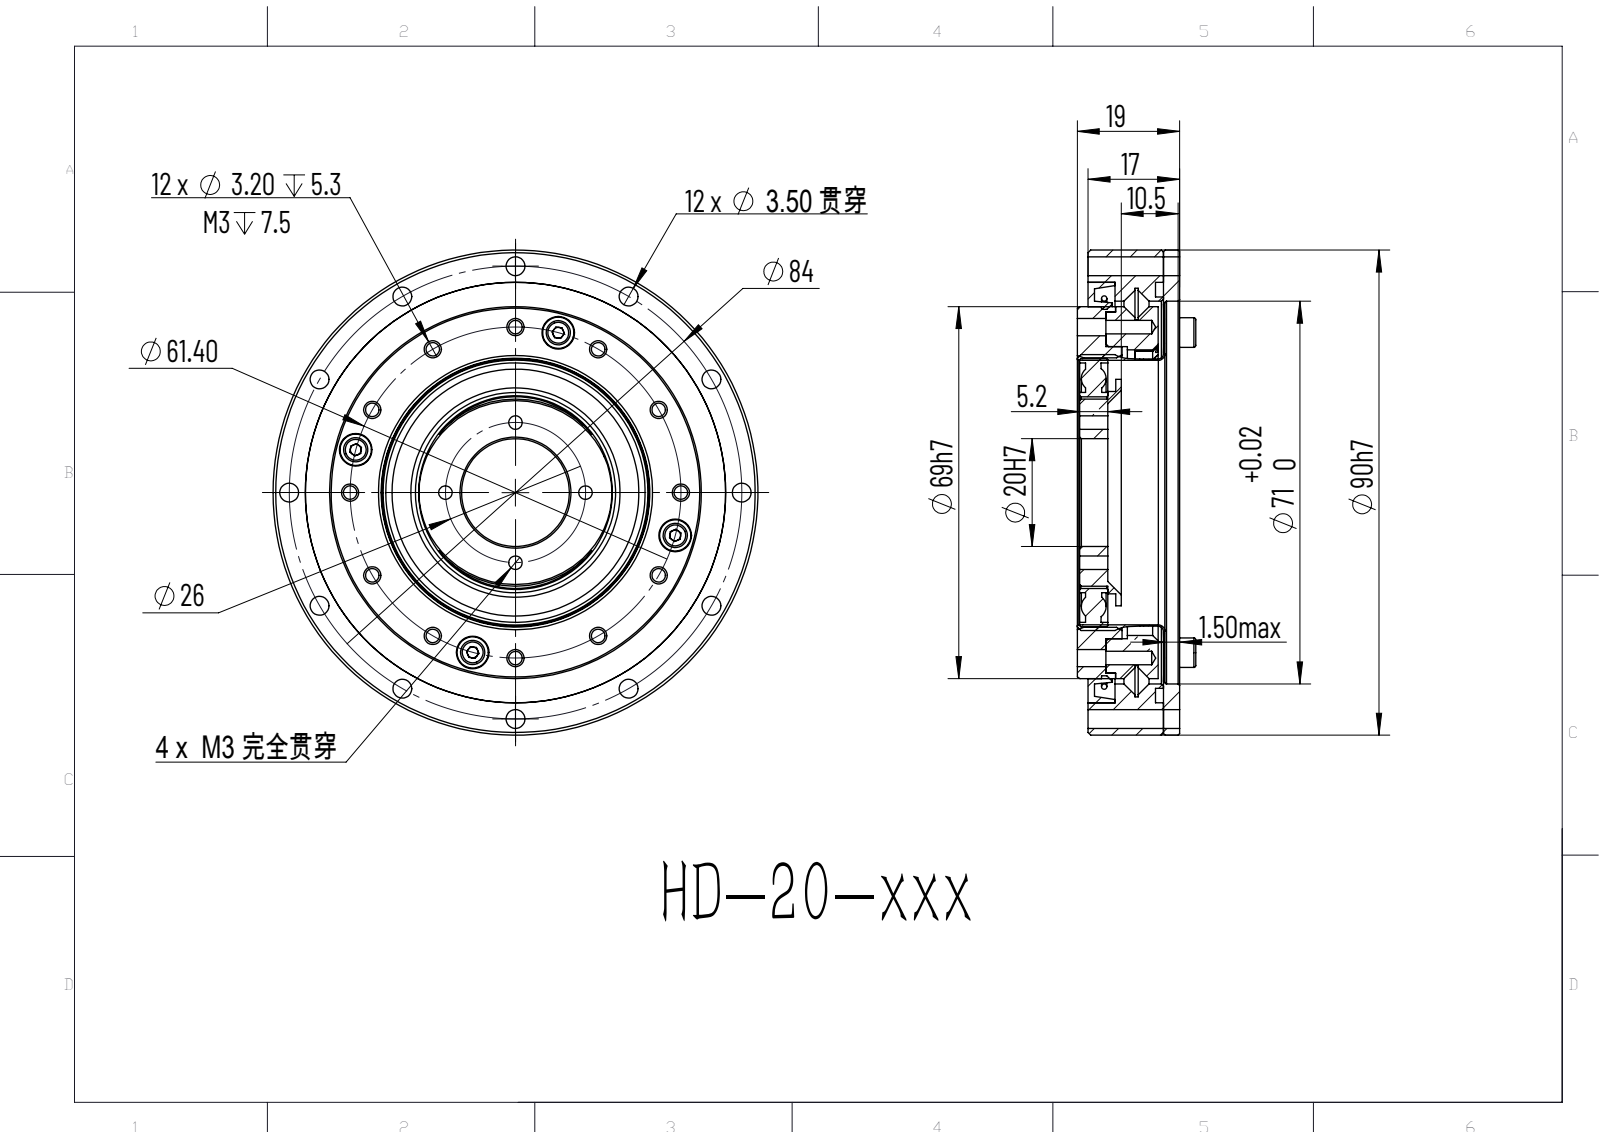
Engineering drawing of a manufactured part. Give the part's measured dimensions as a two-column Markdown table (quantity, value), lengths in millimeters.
| quantity | value |
| --- | --- |
| part name | HD-20-xxx; hexagon socket head cap screws gb_GB_FASTENER_SCREWS_HSHCS M2.5X6-N; hexagon socket head cap screws gb_GB_FASTENER_SCREWS_HSHCS M3X8-C; HD-20???? <1> (+5 more) |
| STEP written by | ONSHAPE BY PTC INC, 1.201 (AP242_MANAGED_MODEL_BASED_3D_ENGINEERING_MIM_LF) |
| units | millimeters |
| bodies | 17 solids, 399 faces (172 planar, 129 cylindrical, 98 other) |
| overall size | 90 × 90 × 22 |
| volume | 68 034 mm³ |
| surface area | 62 046 mm² |
| round holes (diameter × count) | 2.5 × 24, 3.5 × 16, 3.2 × 12, 3.4 × 4, 5.8 × 4, 2.05 × 1, 2.9 × 1, 5 × 1, 20 × 1, 35.56 × 1, 48.13 × 1, 49.07 × 1 |
| round bosses / shafts (diameter × count) | 5.5 × 4, 4.5 × 4, 3 × 4, 90 × 1, 72.6 × 1, 69 × 1, 64.19 × 1, 51.19 × 1 |
| main face-to-face distances | 14, 3, 17, 10.7, 13.7, 3.3, 2.74, 10.96, 14.26, 2 |
| hole center spacings | 42, 21.75, 63.21, 30.7, 70.28, 21.74, 37.64, 52.02 |
